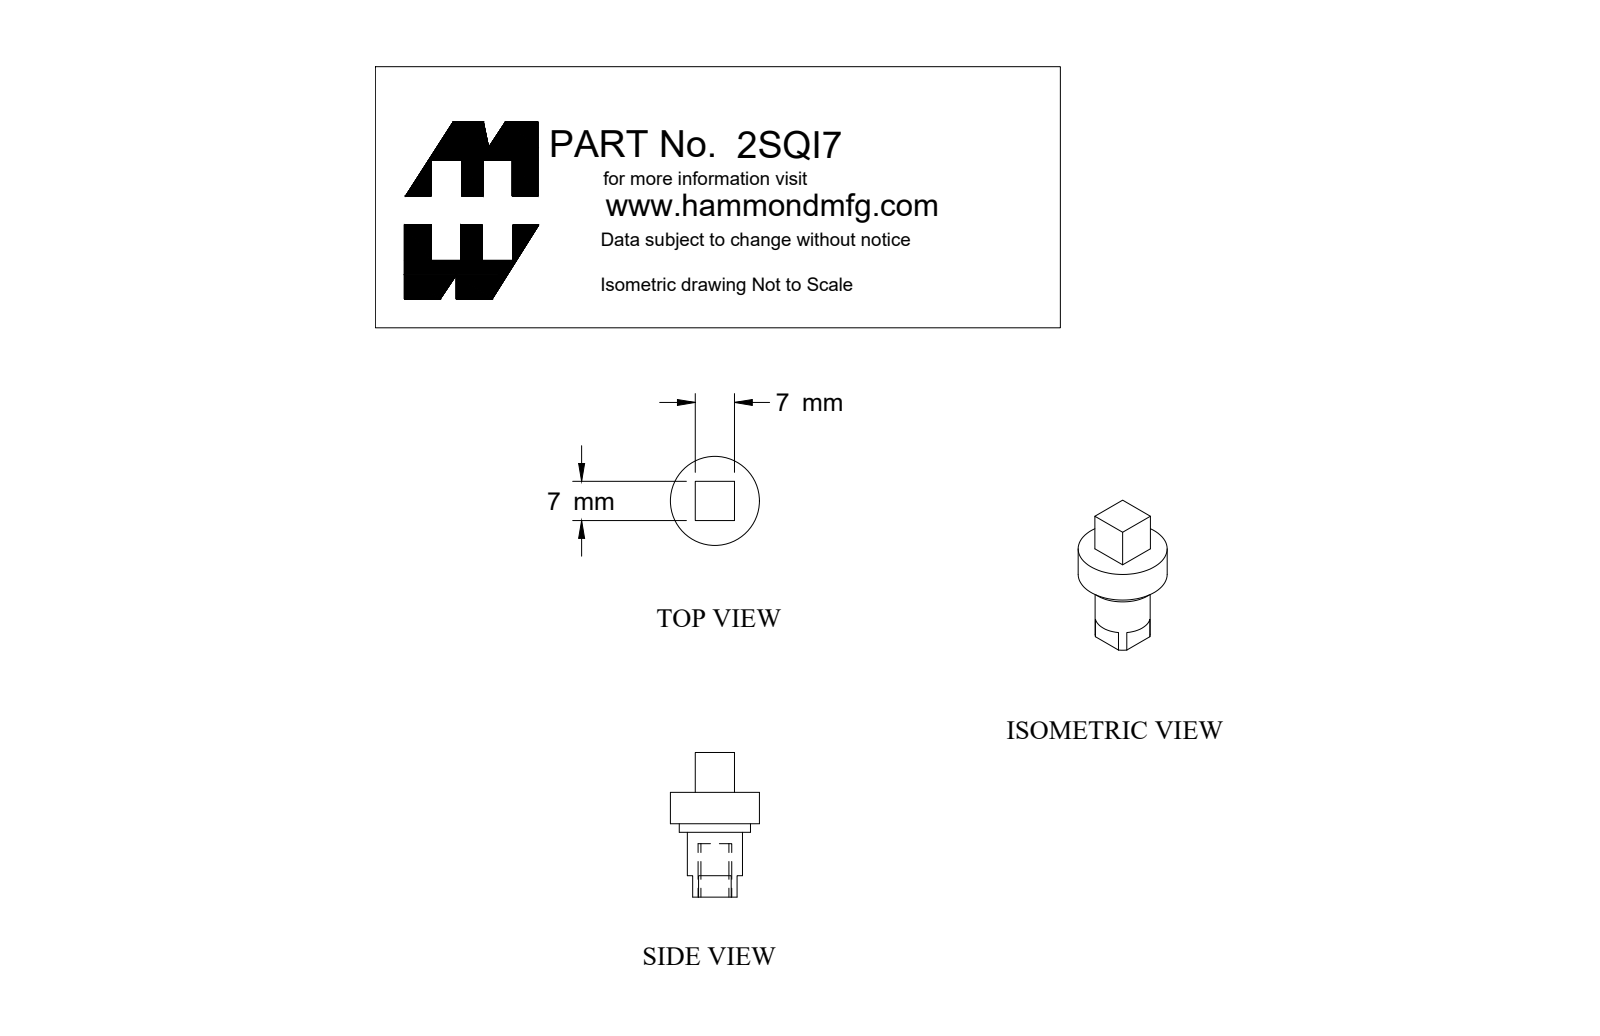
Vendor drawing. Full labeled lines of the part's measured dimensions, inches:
Part name (STEP PRODUCT): 2SQI7
STEP written by: SolidWorks 2018 (AUTOMOTIVE_DESIGN)
Units: inches
Bodies: 1 solid, 22 faces (18 planar, 4 cylindrical, 0 other)
Overall size (bounding box): 1.015 × 0.625 × 0.625
Volume: 0.139 in³ · Surface area: 2.224 in²
Round holes (diameter × count): ⌀0.197 ×1
Round bosses / shafts (diameter × count): ⌀0.625 ×1, ⌀0.5 ×1, ⌀0.387 ×1
Main face-to-face distances: 0.28, 0.276, 0.018, 0.294, 0.22, 0.06, 0.56, 0.5, 0.312, 0.455
